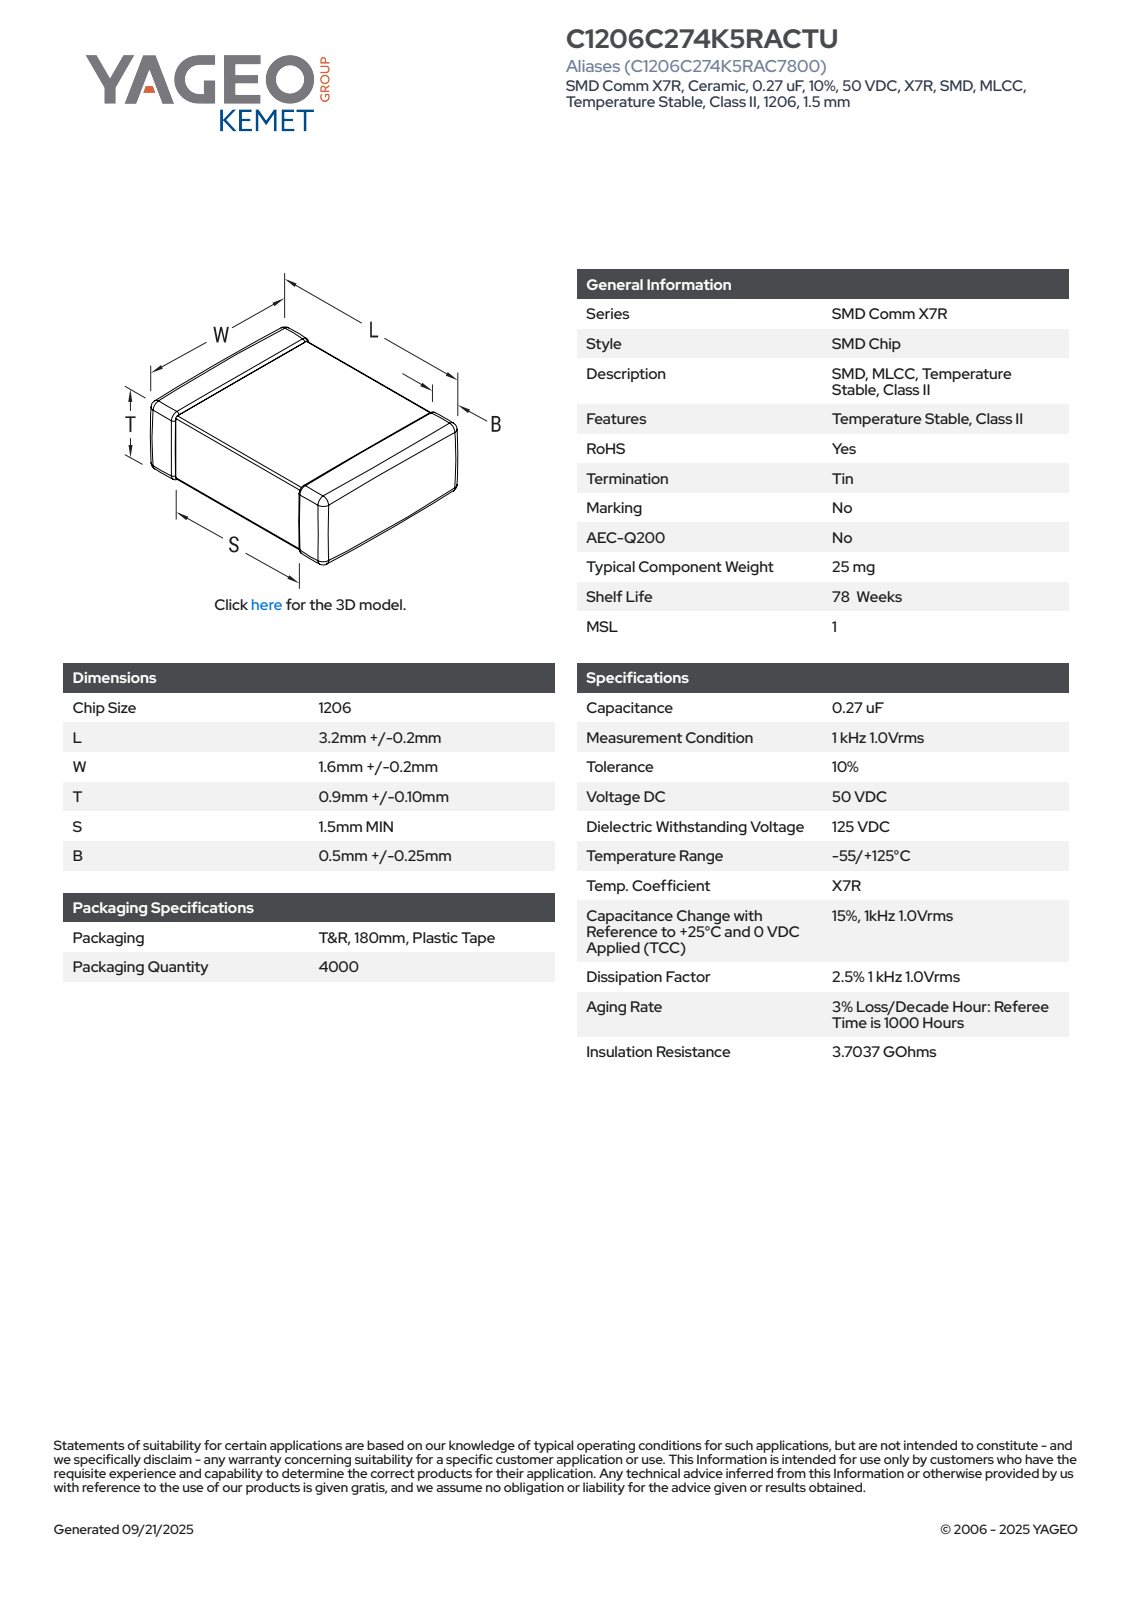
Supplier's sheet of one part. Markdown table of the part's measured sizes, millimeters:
| quantity | value |
| --- | --- |
| part name | CCS_CCSTDNOS_1206_L3.4W1.8T1B0.75 |
| STEP written by | SolidWorks 2014 (AUTOMOTIVE_DESIGN) |
| units | millimeters |
| bodies | 4 solids, 125 faces (71 planar, 38 cylindrical, 16 other) |
| overall size | 3.4 × 1.8 × 1 |
| volume | 6 mm³ |
| surface area | 22 mm² |
| main face-to-face distances | 0.96, 0.92, 1.76, 1, 1.72, 3.4, 1.8, 0.97, 0.93, 0.99 |
